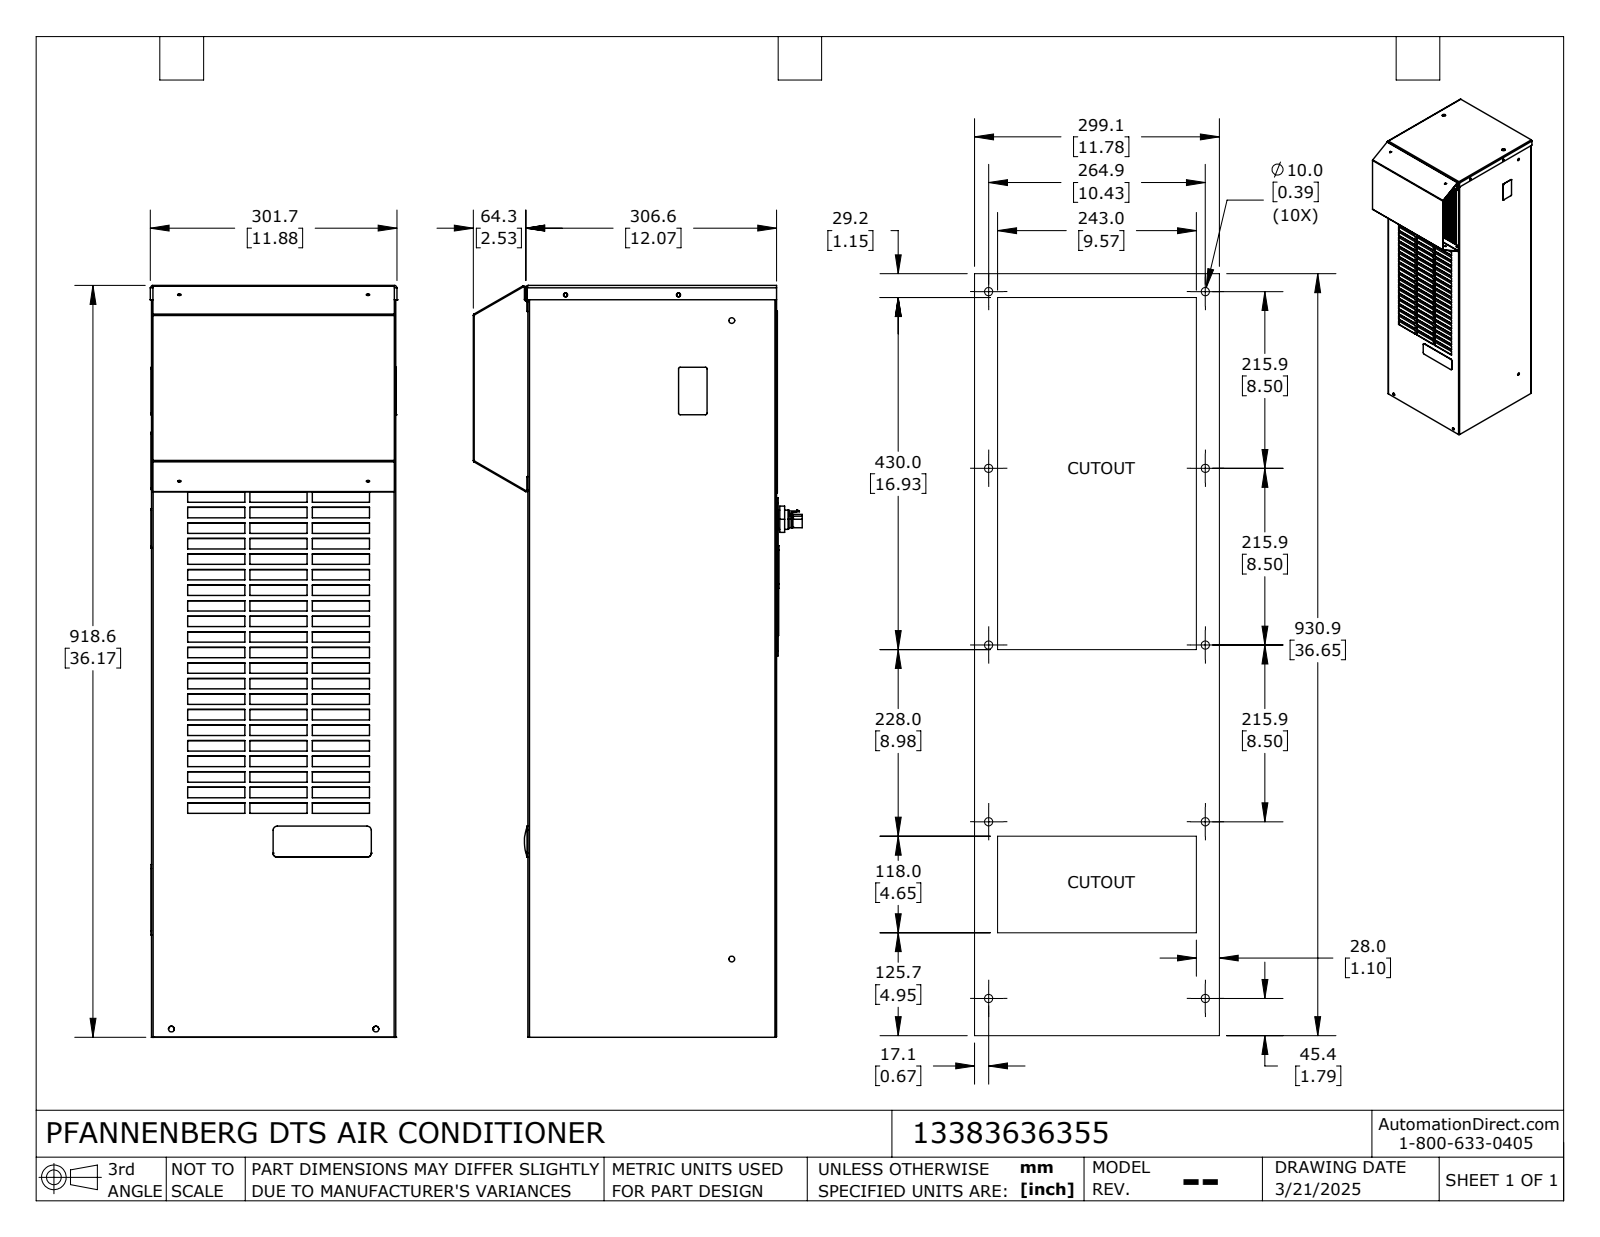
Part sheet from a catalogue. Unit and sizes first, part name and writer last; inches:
Units: inches
Overall size (bounding box): 36.166 × 15.829 × 11.878
Round holes (diameter × count): ⌀0.165 ×35, ⌀0.189 ×10, ⌀0.276 ×6, ⌀0.169 ×5, ⌀0.209 ×5, ⌀0.122 ×4, ⌀0.161 ×4, ⌀0.17 ×2, ⌀0.203 ×2, ⌀0.394 ×2, ⌀0.945 ×2, ⌀0.315 ×1
Round bosses / shafts (diameter × count): ⌀0.079 ×4, ⌀0.866 ×2, ⌀1.378 ×1, ⌀0.906 ×1
Partial cylindrical surfaces — rounded edges, fillets, slot ends (radius × count): R0.125 ×112, R0.031 ×19, R0.079 ×12, R0.197 ×12, R0.087 ×10, R0.236 ×10, R0.076 ×8, R0.078 ×4
Main face-to-face distances: 11.811, 11.752, 0.045, 11.843, 0.031, 11.888, 0.076, 0.056, 0.028, 11.839
Hole centre spacings: 0.294, 4.398, 6.602, 0.244, 0.231, 0.254, 0.454, 0.755
Volume: 4 957 in³ · Surface area: 4 044 in²
Bodies: 1 solid, 1788 faces (1242 planar, 493 cylindrical, 53 other)
Part name (STEP PRODUCT): 13383636355_Default
STEP written by: SolidWorks 2024 (CONFIG_CONTROL_DESIGN)
